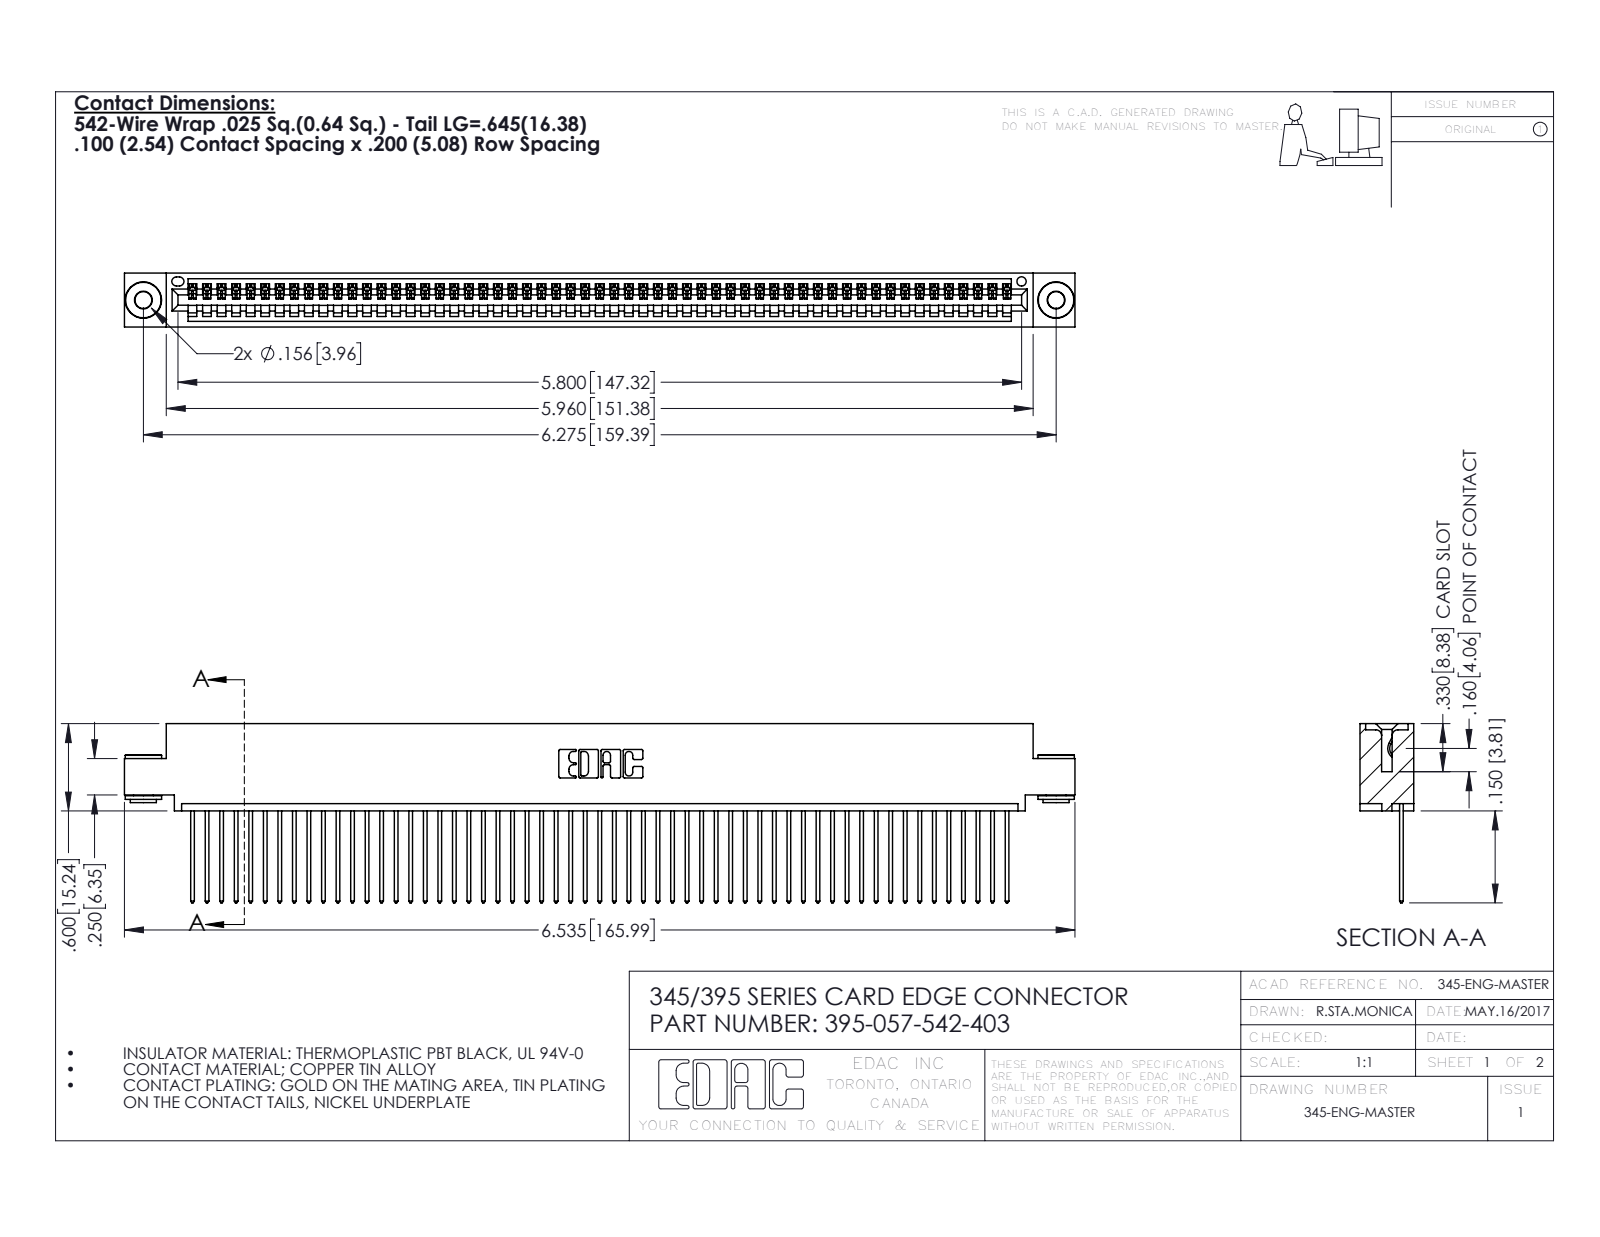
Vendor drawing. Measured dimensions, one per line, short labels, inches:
name: 345-292-001_345-293-142; 345-250-002_345-250-002-102; 395-057-542-403; 345 Part_0.110 Offset - 0.156 Dia-TH
written by: SolidWorks 2016 (CONFIG_CONTROL_DESIGN)
unit: in
bodies: 60 solids, 3474 faces (2374 planar, 1092 cylindrical, 8 other)
size: 6.535 × 1.232 × 0.37
volume: 0.974 in³; area: 34.9 in²
holes: 2× ⌀0.116, 2× ⌀0.156, 1× ⌀0.064
bosses: 2× ⌀0.25, 2× ⌀0.18, 2× ⌀0.136
rounds: 114× R0.006, 114× R0.01, 22× R0.01, 6× R0.007, 6× R0.031, 3× R0.026, 2× R0.031, 2× R0.04
face distances: 0.072, 0.298, 0.025, 0.098, 0.272, 0.37, 0.2, 0.225, 0.149, 0.072
hole spacings: 0.27, 6.039, 6.275
